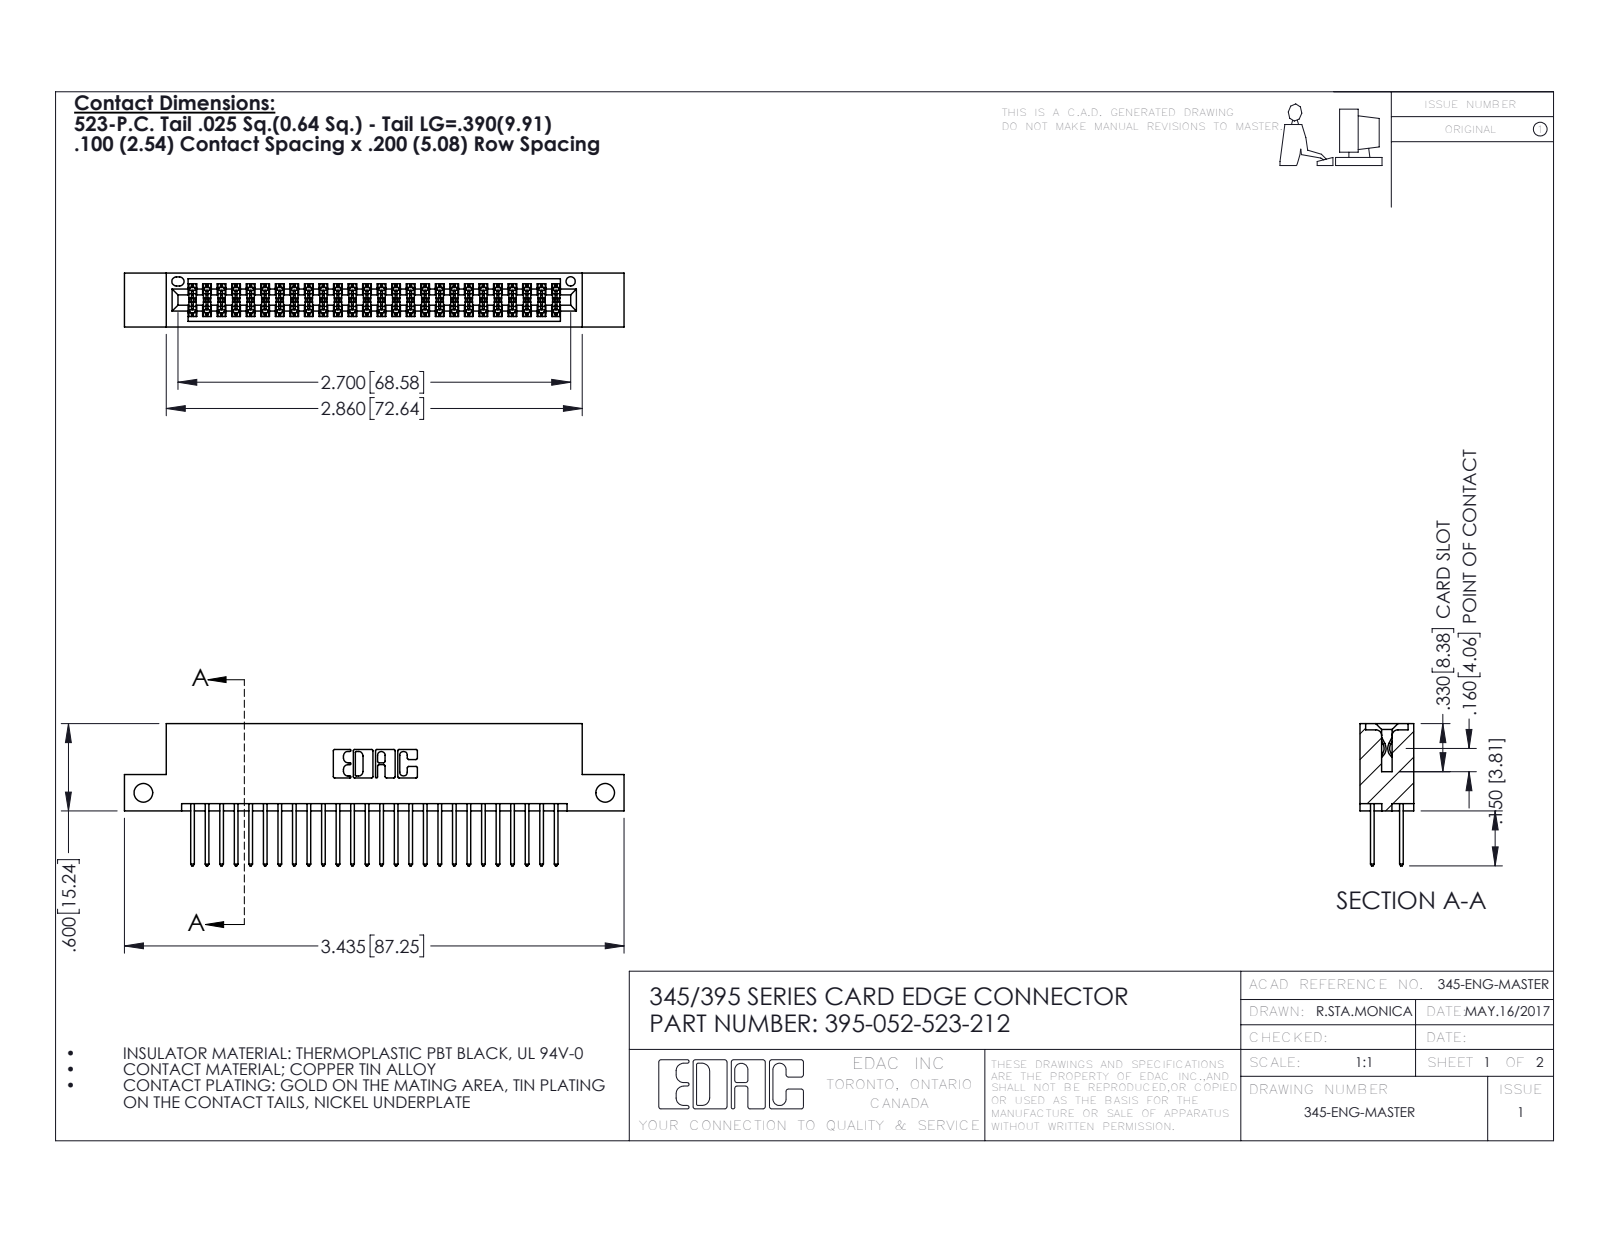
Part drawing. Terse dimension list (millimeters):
name: 345-292-001_345-293-123; 395-052-523-212; 345 Part_Flush Mounting Lugs - Side Mount
written by: SolidWorks 2016 (CONFIG_CONTROL_DESIGN)
unit: mm
bodies: 53 solids, 2726 faces (1796 planar, 930 cylindrical, 0 other)
size: 87.2 × 24.8 × 9.4
volume: 8 340 mm³; area: 12 370 mm²
holes: 2× ⌀3.3, 1× ⌀1.6
rounds: 78× R0.2, 52× R0.3, 22× R0.3, 6× R0.2, 6× R0.8, 3× R0.7, 2× R0.4, 2× R0.5
face distances: 7.6, 1.8, 5.1, 2.5, 6.9, 0.6, 9.4, 5.7, 4.4, 3.8
hole spacings: 80.6
